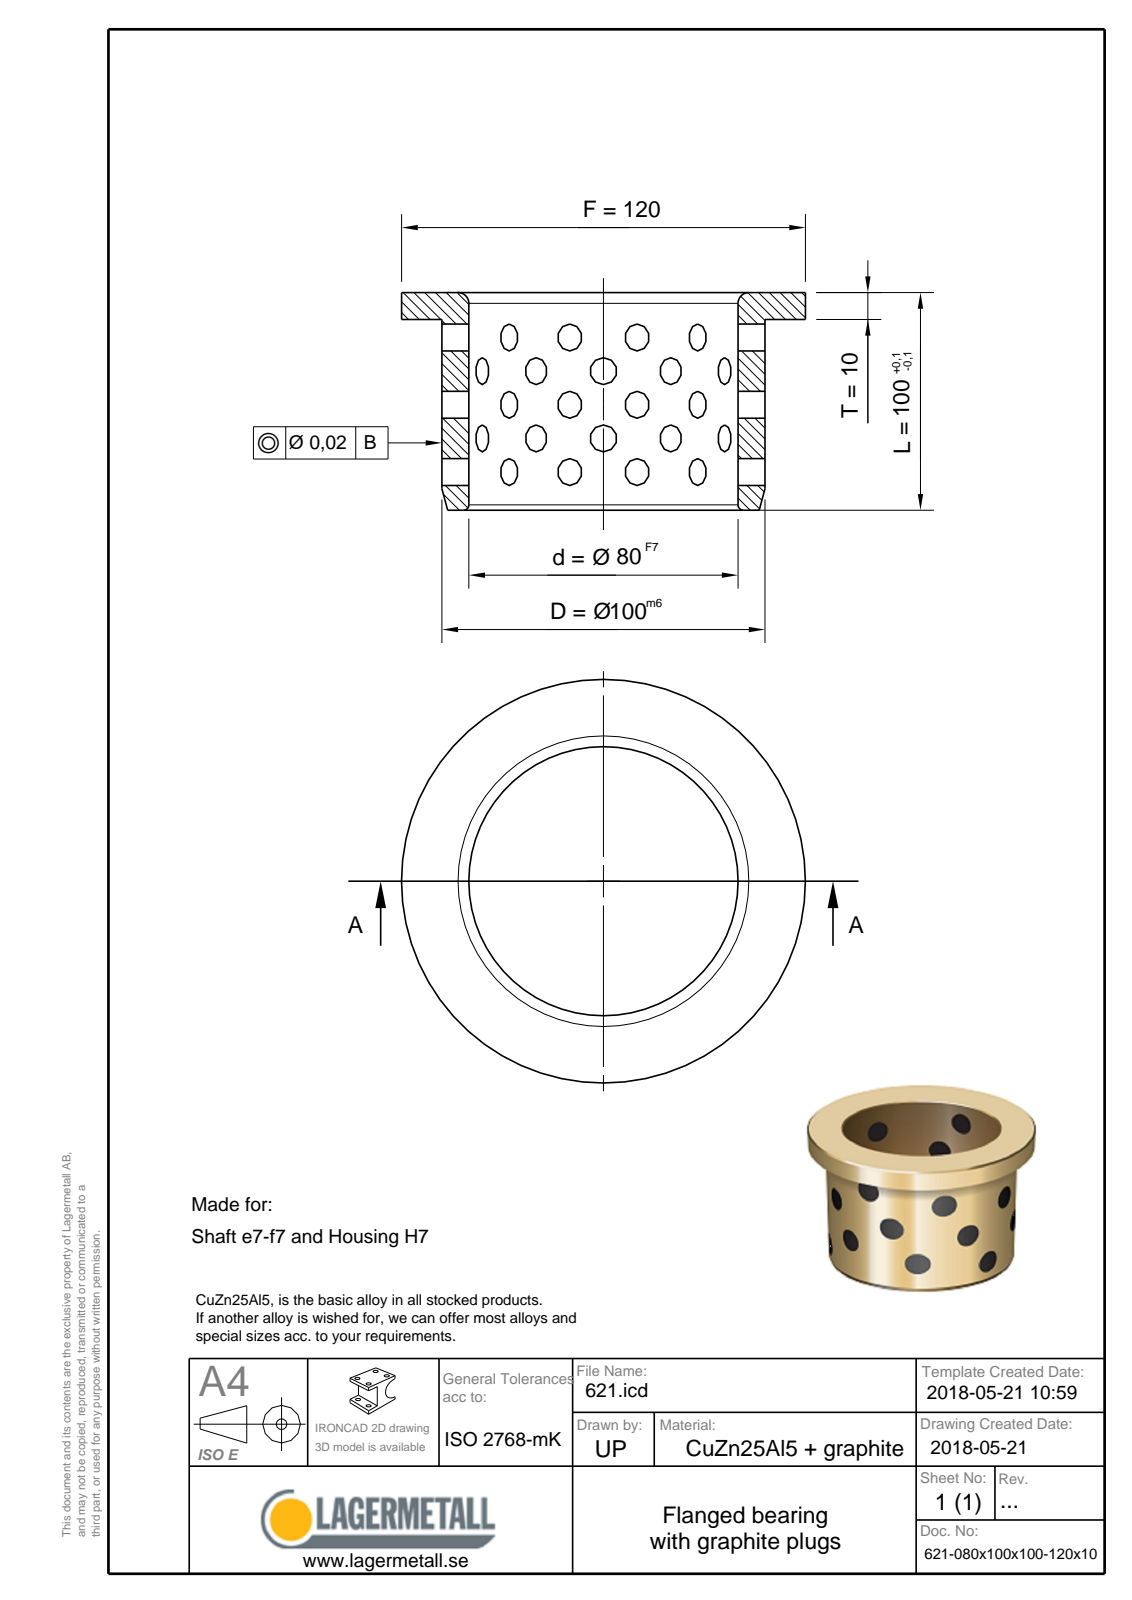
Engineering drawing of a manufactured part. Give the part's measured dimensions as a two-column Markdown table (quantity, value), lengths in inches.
| quantity | value |
| --- | --- |
| part name | 621-080x100x100-120x10 |
| STEP written by | Spatial InterOp 3D (CONFIG_CONTROL_DESIGN) |
| units | inches |
| bodies | 1 solid, 9 faces (3 planar, 3 cylindrical, 3 other) |
| overall size | 4.724 × 4.724 × 3.937 |
| volume | 19.28 in³ |
| surface area | 106.7 in² |
| round holes (diameter × count) | 3.15 × 1 |
| round bosses / shafts (diameter × count) | 4.724 × 1, 3.937 × 1 |
| main face-to-face distances | 0.394, 3.543, 3.937 |
